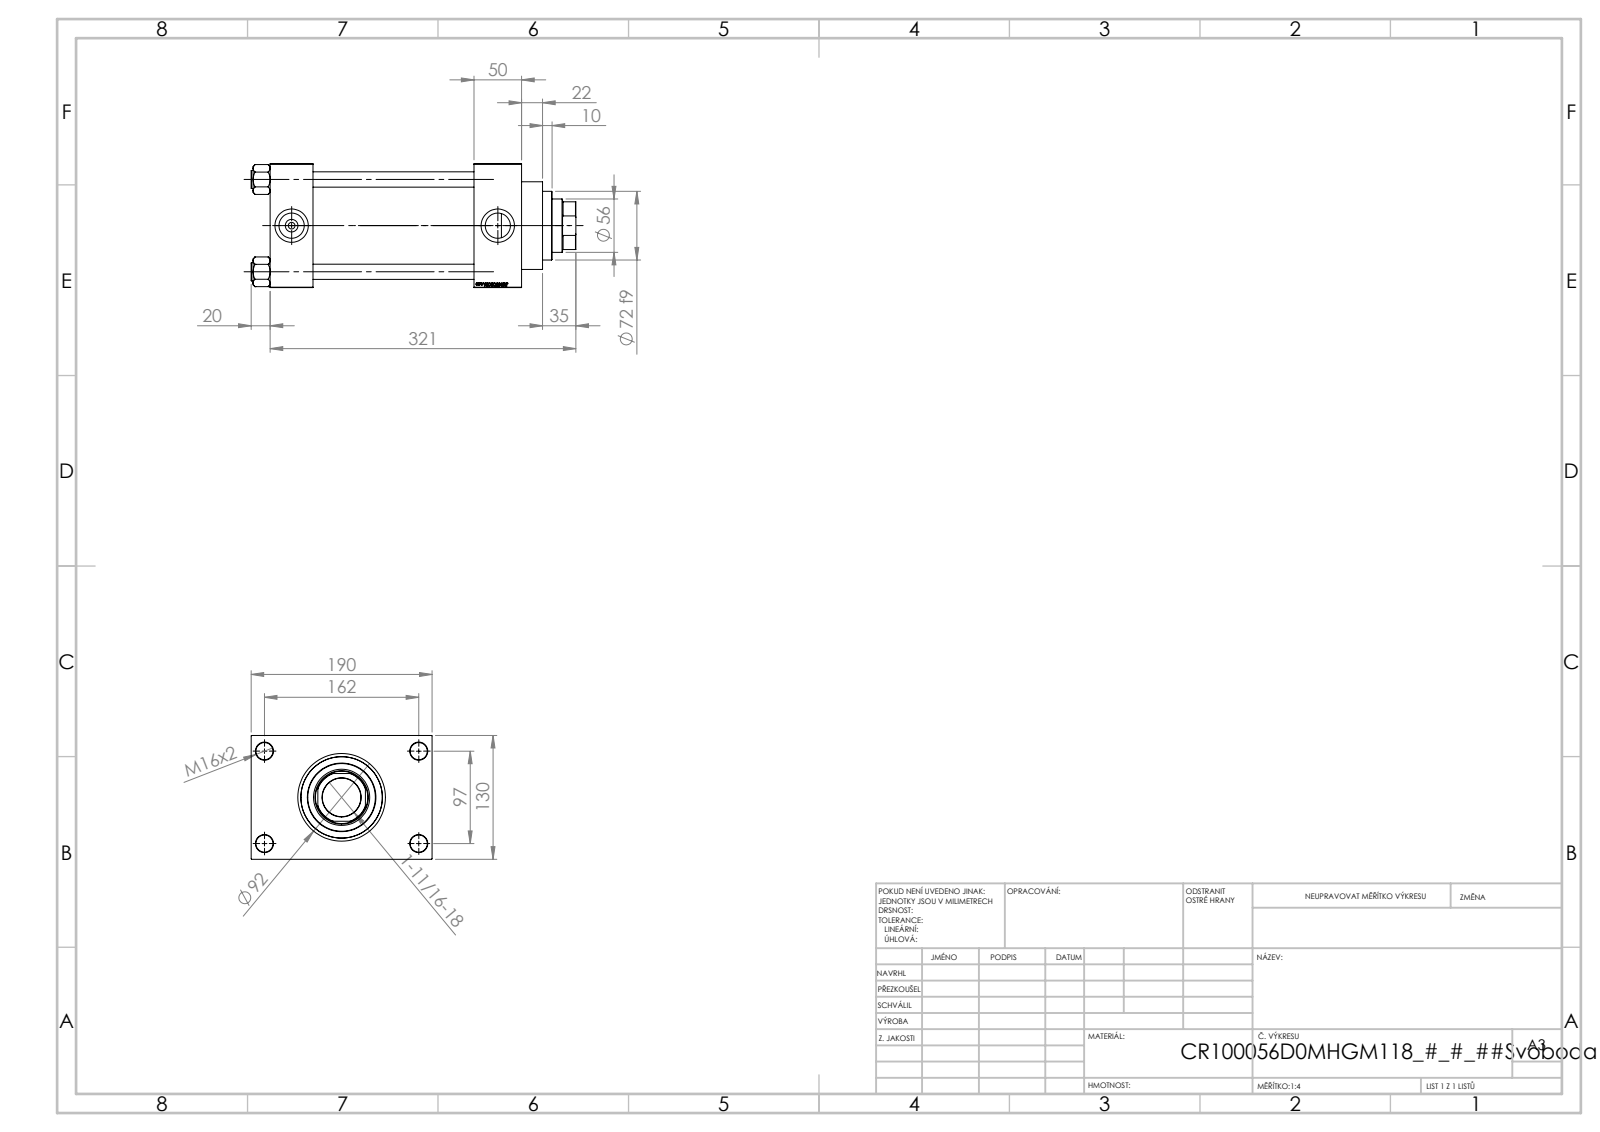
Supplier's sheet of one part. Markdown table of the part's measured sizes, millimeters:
| quantity | value |
| --- | --- |
| part name | V215CR_D_Body; V215CR_VCP_D; NUT_M5_D; V215_VC_A (+1 more) |
| STEP written by | SolidWorks 2019 (CONFIG_CONTROL_DESIGN) |
| units | millimeters |
| bodies | 11 solids, 1151 faces (545 planar, 88 cylindrical, 518 other) |
| overall size | 341 × 190 × 130 |
| volume | 3 043 000 mm³ |
| surface area | 462 731 mm² |
| round holes (diameter × count) | 16 × 4, 18 × 4, 7 × 2, 26.44 × 2, 35 × 2, 40.5 × 1, 56 × 1, 59 × 1, 76 × 1, 85.5 × 1, 100 × 1 |
| round bosses / shafts (diameter × count) | 19 × 4, 106 × 1, 92 × 1, 72 × 1 |
| partial cylindrical surfaces (radius × count) | 27 × 1 |
| main face-to-face distances | 130, 50, 45, 214, 169, 264, 219, 30, 160, 190 |
| hole center spacings | 32.55, 68.52, 94.41, 96.9, 102.27, 129.45, 161.73, 97 |
